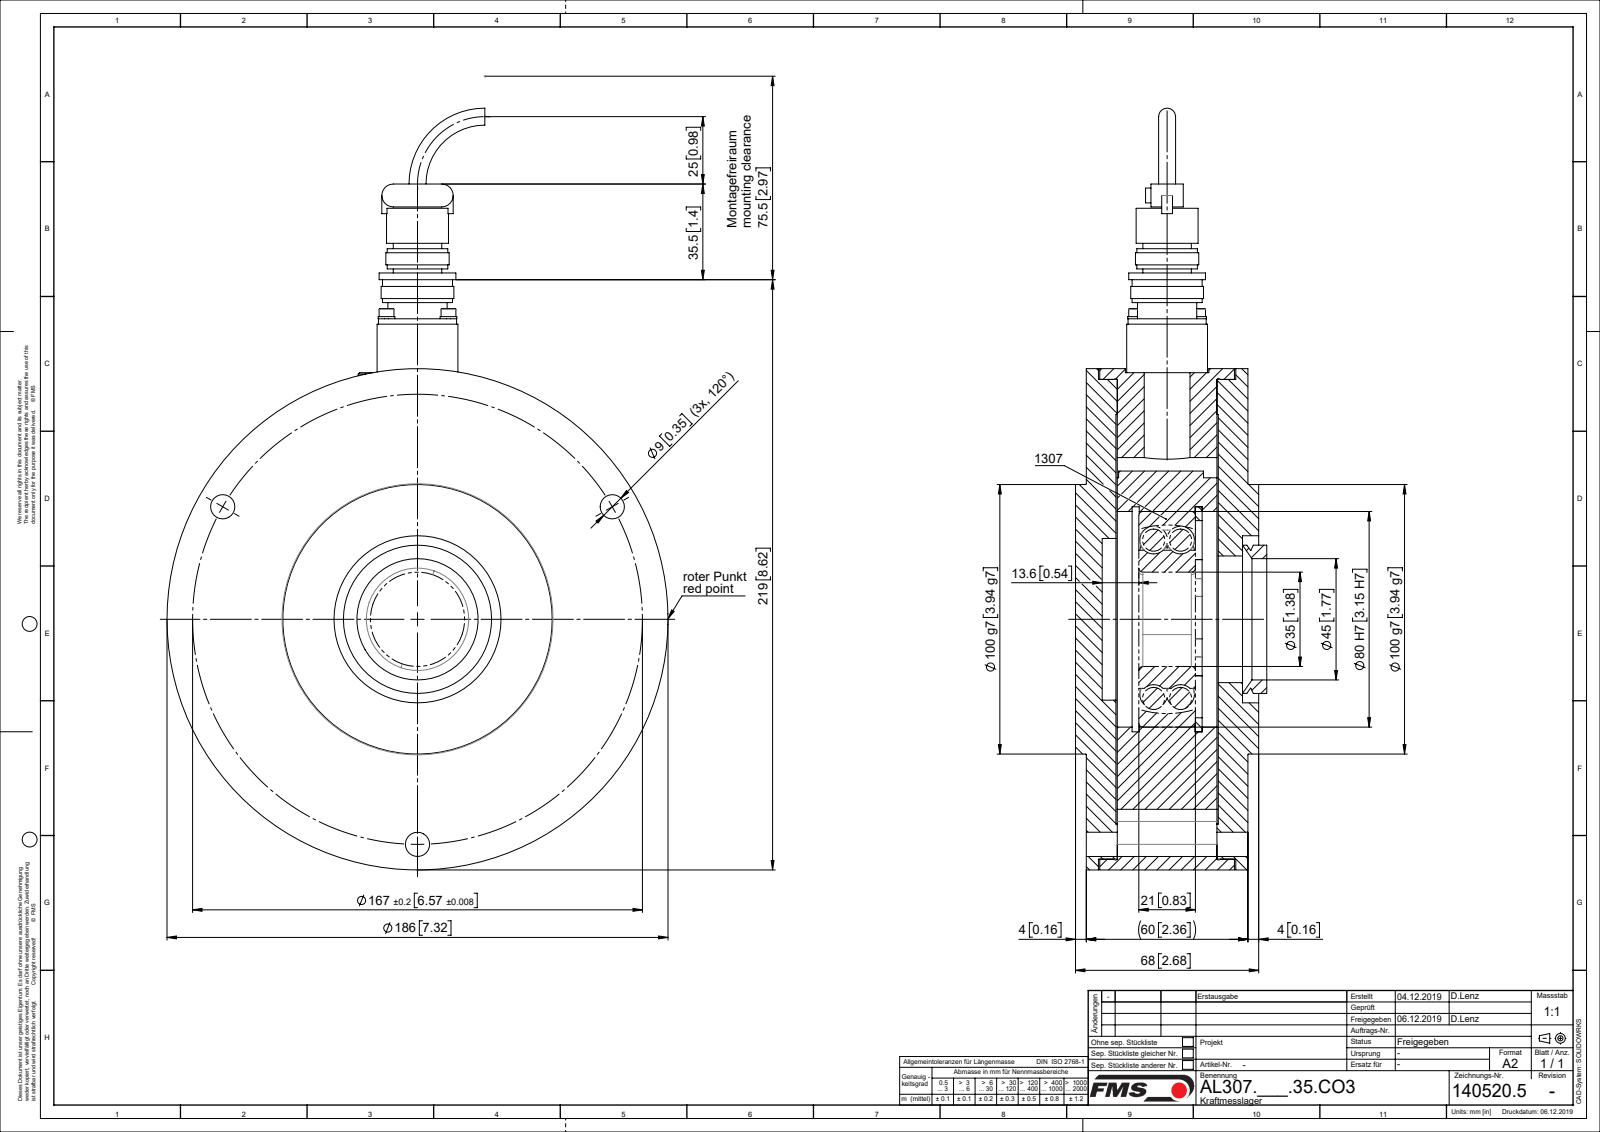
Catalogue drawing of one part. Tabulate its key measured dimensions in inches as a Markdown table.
| quantity | value |
| --- | --- |
| part name | FLANSCHDOSE_14S-2P_4-POLIG; 130419.6_01; 49026_01; Federringe_DIN127A_M03 (+7 more) |
| STEP written by | SolidWorks 2018 (CONFIG_CONTROL_DESIGN) |
| units | inches |
| bodies | 45 solids, 470 faces (132 planar, 210 cylindrical, 128 other) |
| overall size | 11.128 × 7.323 × 2.795 |
| volume | 91.6 in³ |
| surface area | 439.7 in² |
| round holes (diameter × count) | 0.354 × 10, 0.098 × 4, 0.122 × 4, 0.134 × 4, 0.118 × 2, 0.157 × 1, 0.669 × 1, 0.906 × 1, 1.378 × 1, 1.772 × 1, 1.85 × 1, 2.362 × 1 |
| round bosses / shafts (diameter × count) | 0.217 × 6, 0.244 × 4, 0.118 × 4, 0.098 × 4, 7.323 × 1, 3.937 × 1, 2.165 × 1, 2.018 × 1 |
| partial cylindrical surfaces (radius × count) | 0.004 × 4, 0.177 × 3, 0.167 × 2, 0.193 × 2, 1.309 × 1 |
| main face-to-face distances | 0.453, 1.909, 0.02, 1.929, 0.433, 1.476, 1.457, 0.591, 2.362, 1.496 |
| hole center spacings | 3.287, 5.694, 0.64, 0.906, 0.996, 2.348, 2.657, 3.653 |
